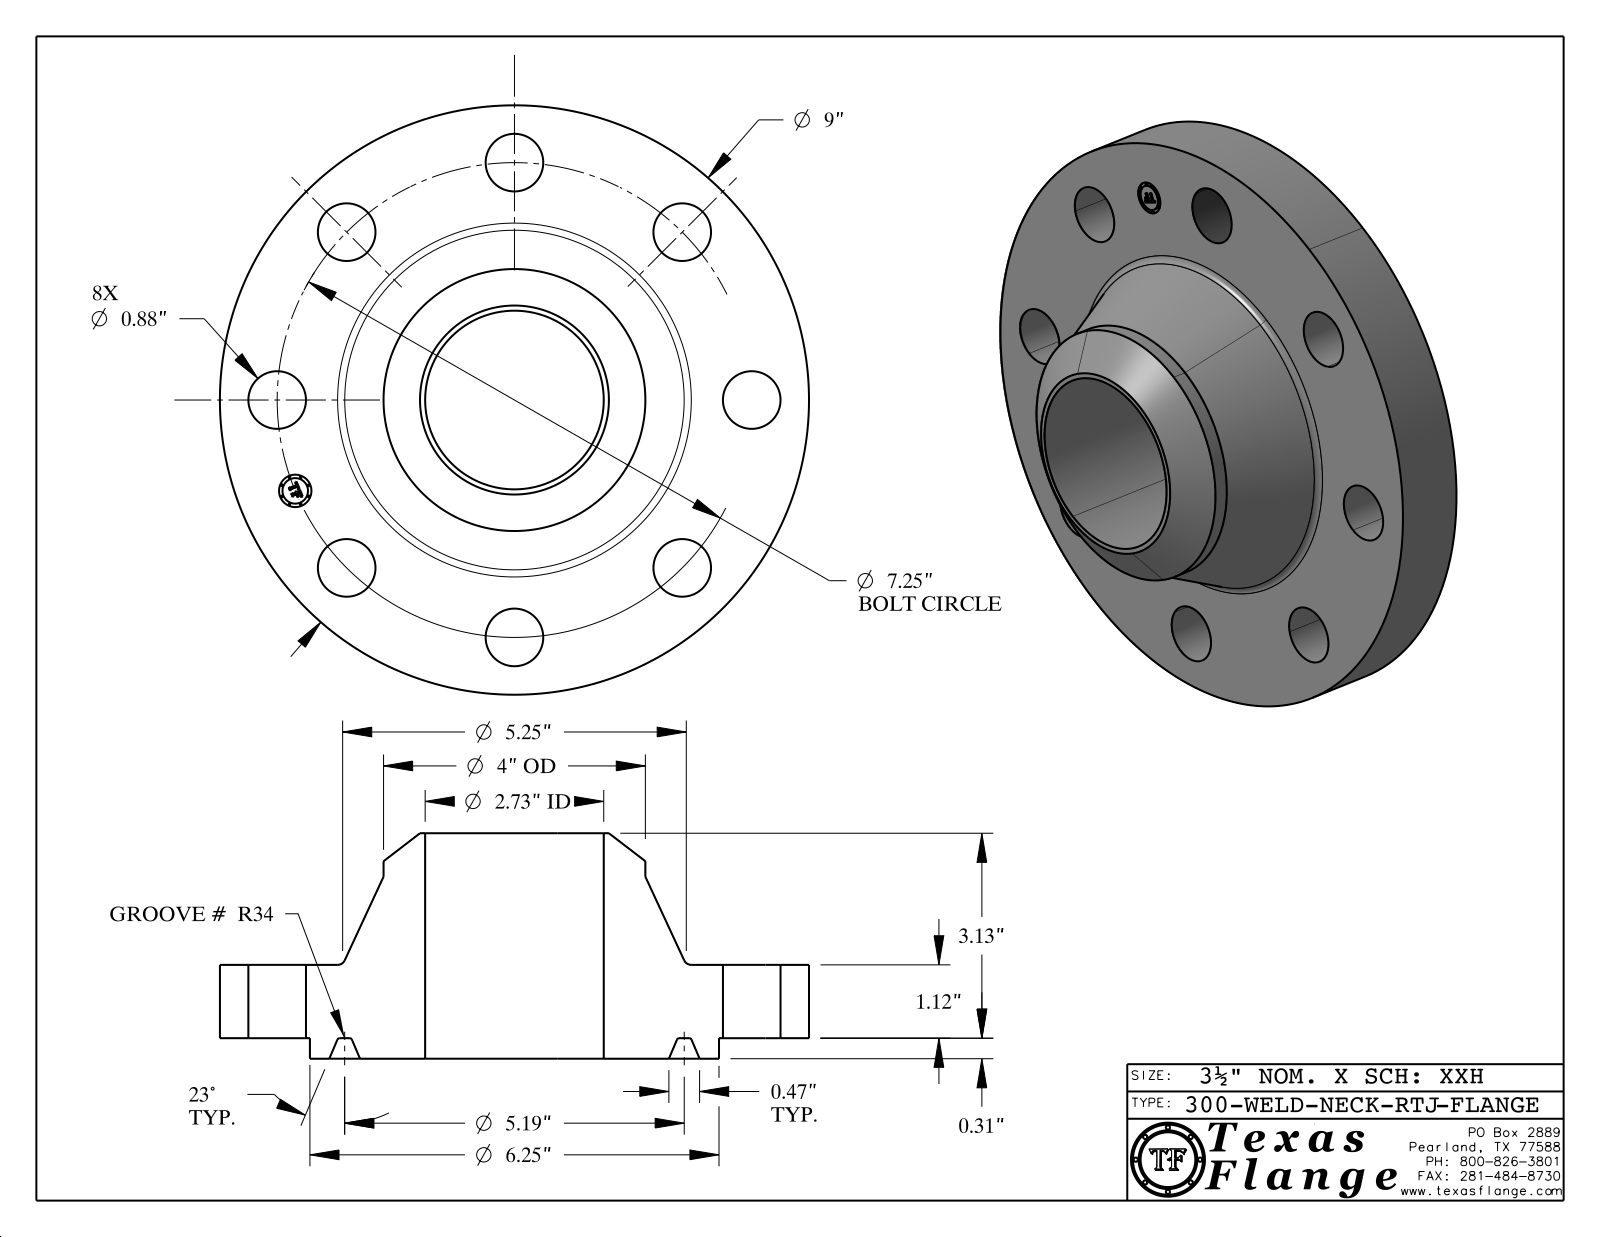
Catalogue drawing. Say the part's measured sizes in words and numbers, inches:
The part is named "300-WELD-NECK-RTJ". Its 3-D file was written by "CATIA V5 STEP AP214 (AUTOMOTIVE_DESIGN)". It is 1 solid with 429 faces: 371 planar, 44 cylindrical and 14 other. Overall it measures 9 by 9 by 3.443 inches. Its volume is 83.32 cubic inches and its surface area 221.3 square inches. Round holes: 8 of diameter 0.88, 1 of diameter 0.495, 1 of diameter 2.728. Round bosses or shafts: 8 of diameter 0.03, 1 of diameter 9, 1 of diameter 6.25, 1 of diameter 4, 1 of diameter 0.39. The main face-to-face distances are 1.12, 0.313, 1.433, 3.443, 3.13, 2.01, 1.418, 1.105, 0.015, 2.025. The hole center spacings are 3.625, 2.774, 5.127, 6.698, 7.25, 1.415, 7.111, 4.028.
